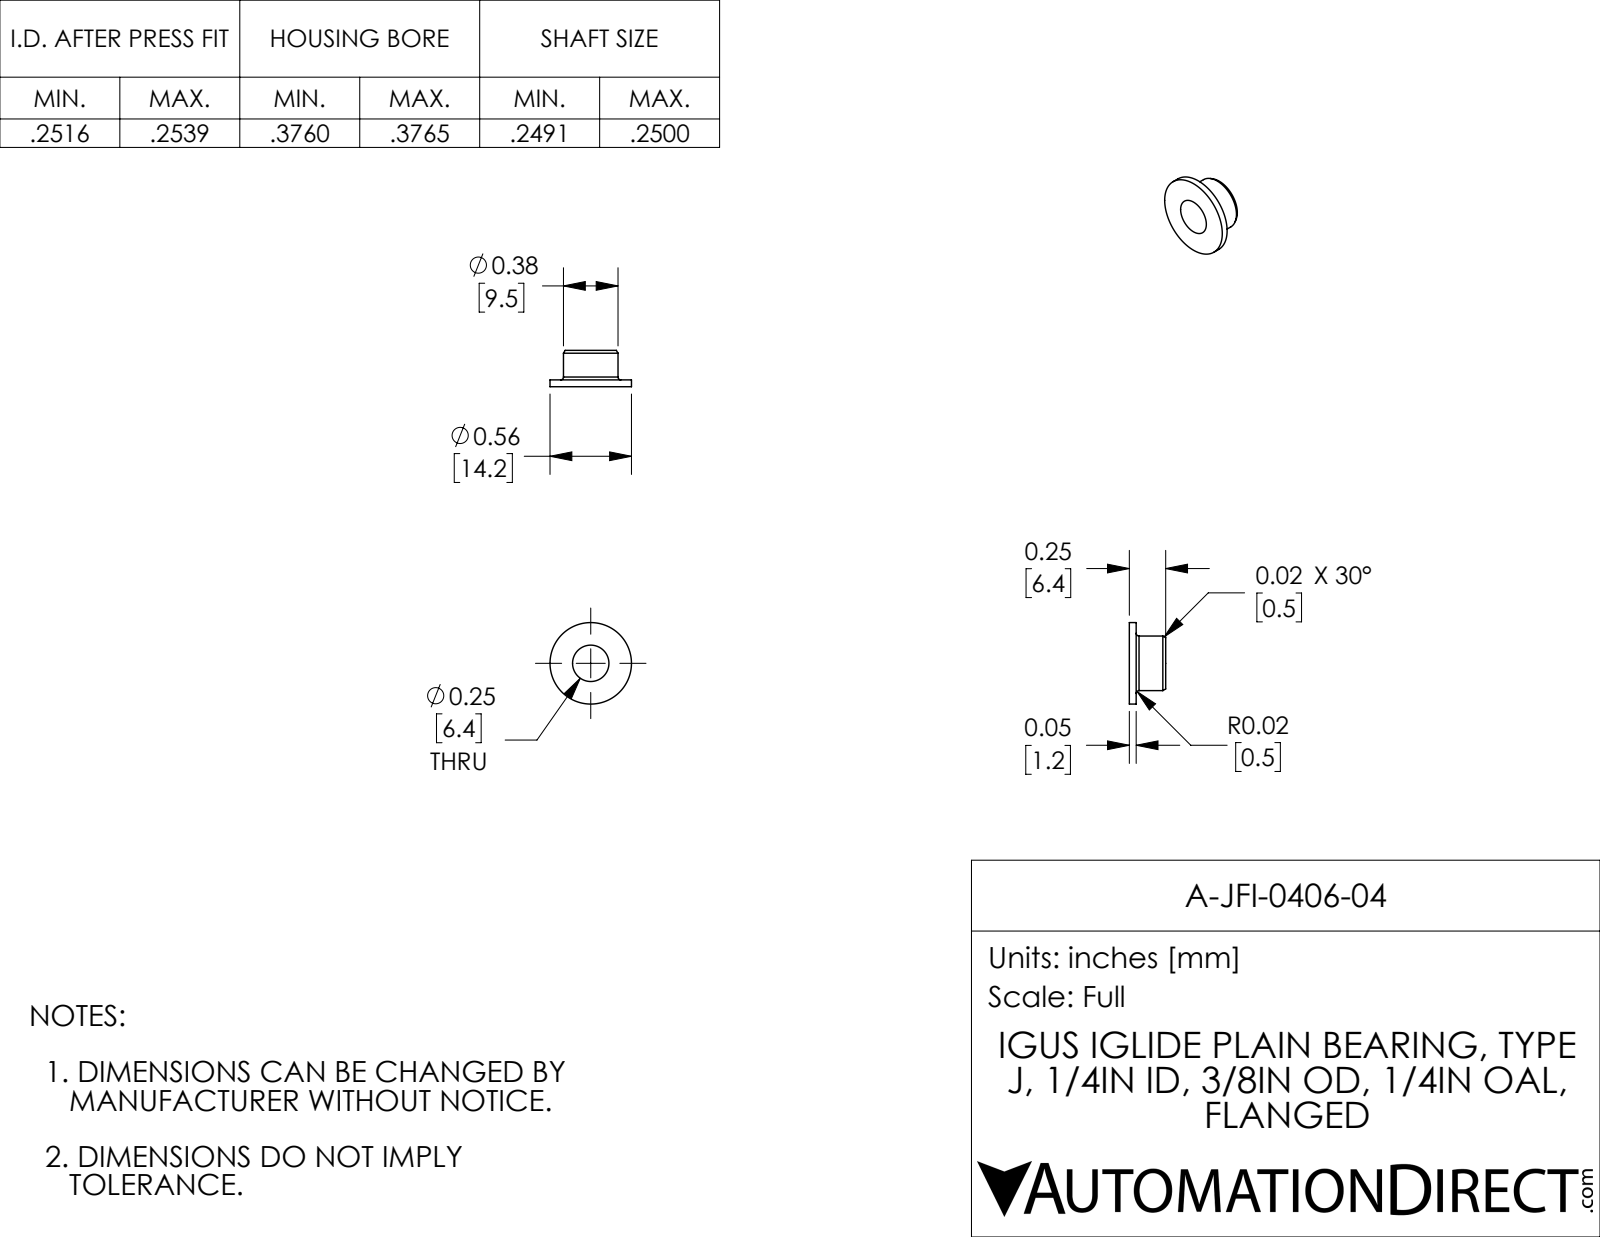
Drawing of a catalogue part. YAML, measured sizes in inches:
part_name: "A-JFI-0406-04"
step_written_by: "SolidWorks 2017 (AUTOMOTIVE_DESIGN)"
units: inches
bodies: {solids: 1, faces: 13, planar: 3, cylindrical: 6, other: 4}
overall_size: [0.56, 0.56, 0.25]
volume: 0.022
surface_area: 0.893
round_holes:
  - {diameter: 0.25, count: 1}
round_bosses_or_shafts:
  - {diameter: 0.56, count: 1}
  - {diameter: 0.375, count: 1}
face_to_face_distances: [0.047, 0.25, 0.203]
